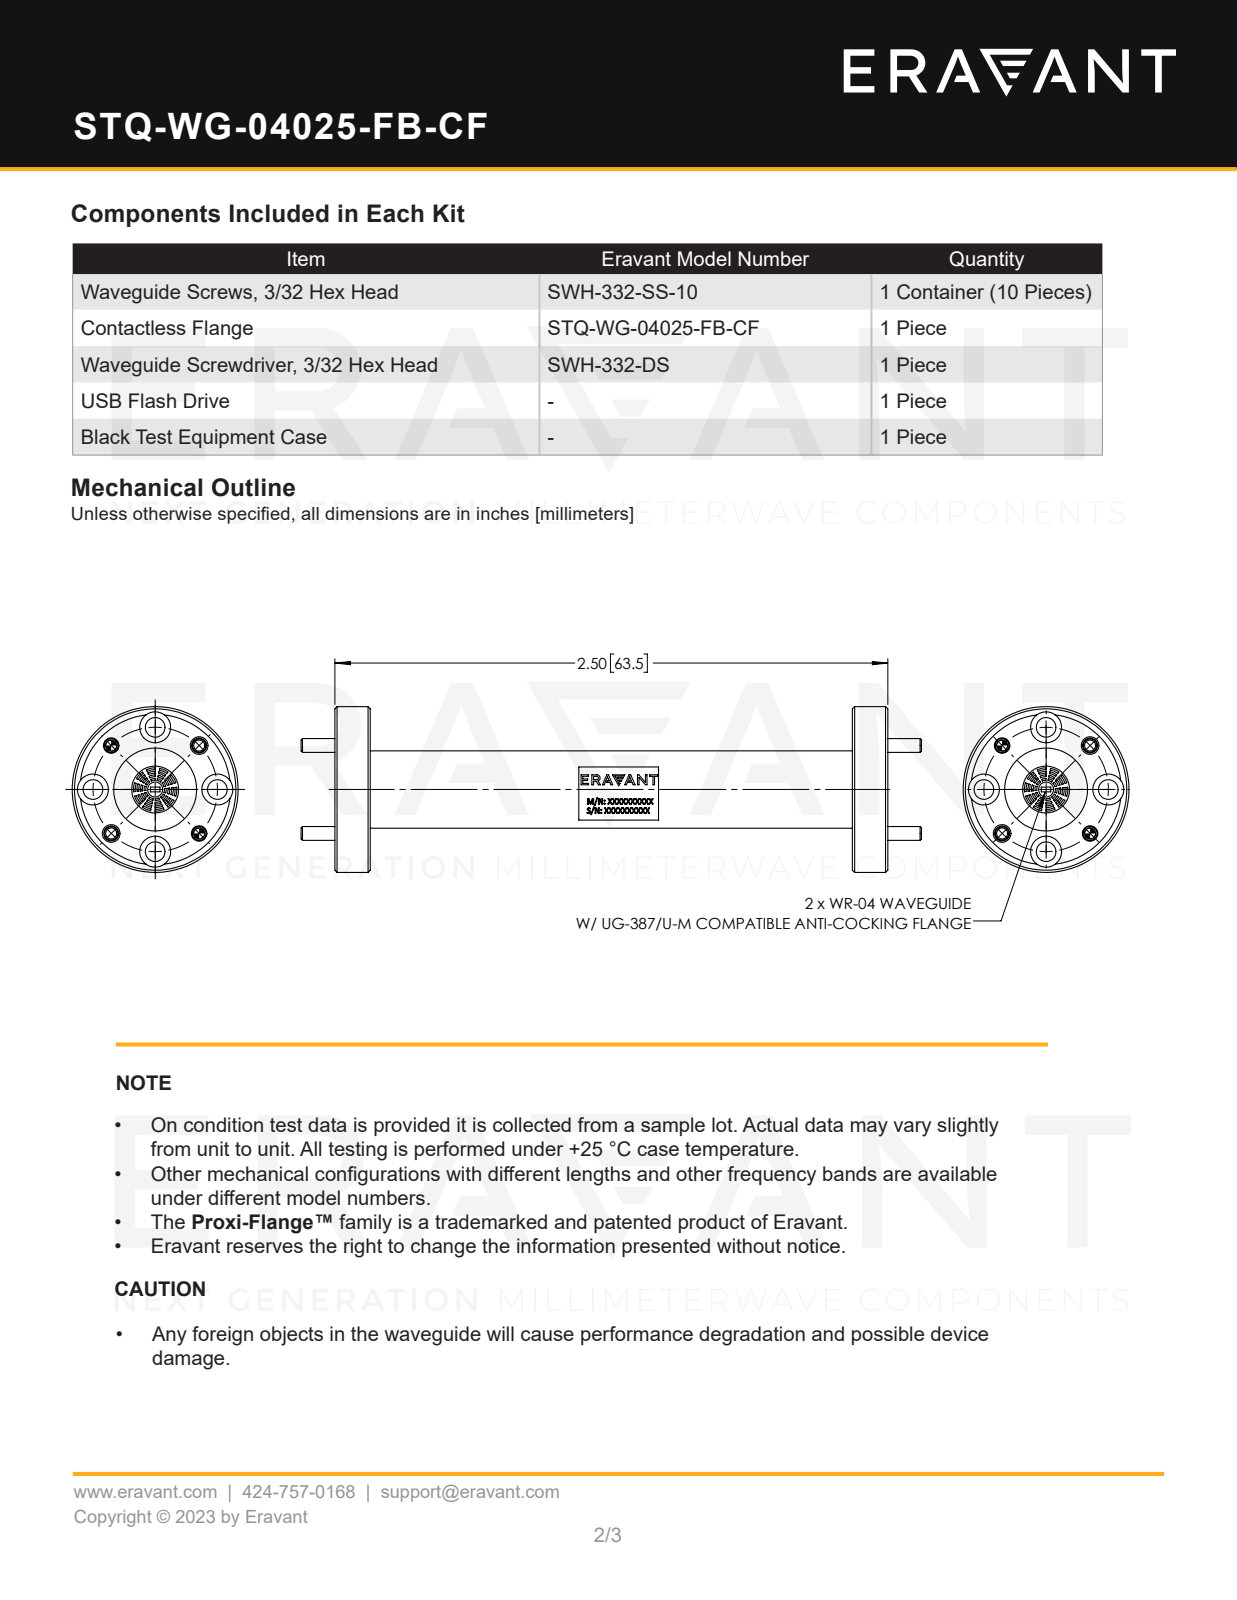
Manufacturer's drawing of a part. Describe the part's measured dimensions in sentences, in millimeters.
The part is named "WG-F04-A-CF". Its 3-D file was written by "SolidWorks 2021 (AUTOMOTIVE_DESIGN)". It is 5 solids with 148 faces: 34 planar, 74 cylindrical and 40 other. Overall it measures 71.2 by 19.1 by 19.1 millimeters. Its volume is 5 420 cubic millimeters and its surface area 3 549 square millimeters. Round holes: 4 of diameter 1.5, 4 of diameter 1.6, 4 of diameter 2.3, 4 of diameter 3.6, 1 of diameter 17.3. Round bosses or shafts: 4 of diameter 1.6, 1 of diameter 19.1, 1 of diameter 9.5, 1 of diameter 8.9. The main face-to-face distances are 3.6, 58.9, 55.4, 62.5, 63, 0.5, 4.1, 59.4, 63.5, 63. The hole center spacings are 5.5, 10.1, 7.1, 13.2, 13.2, 7.1, 14.3, 14.3.
